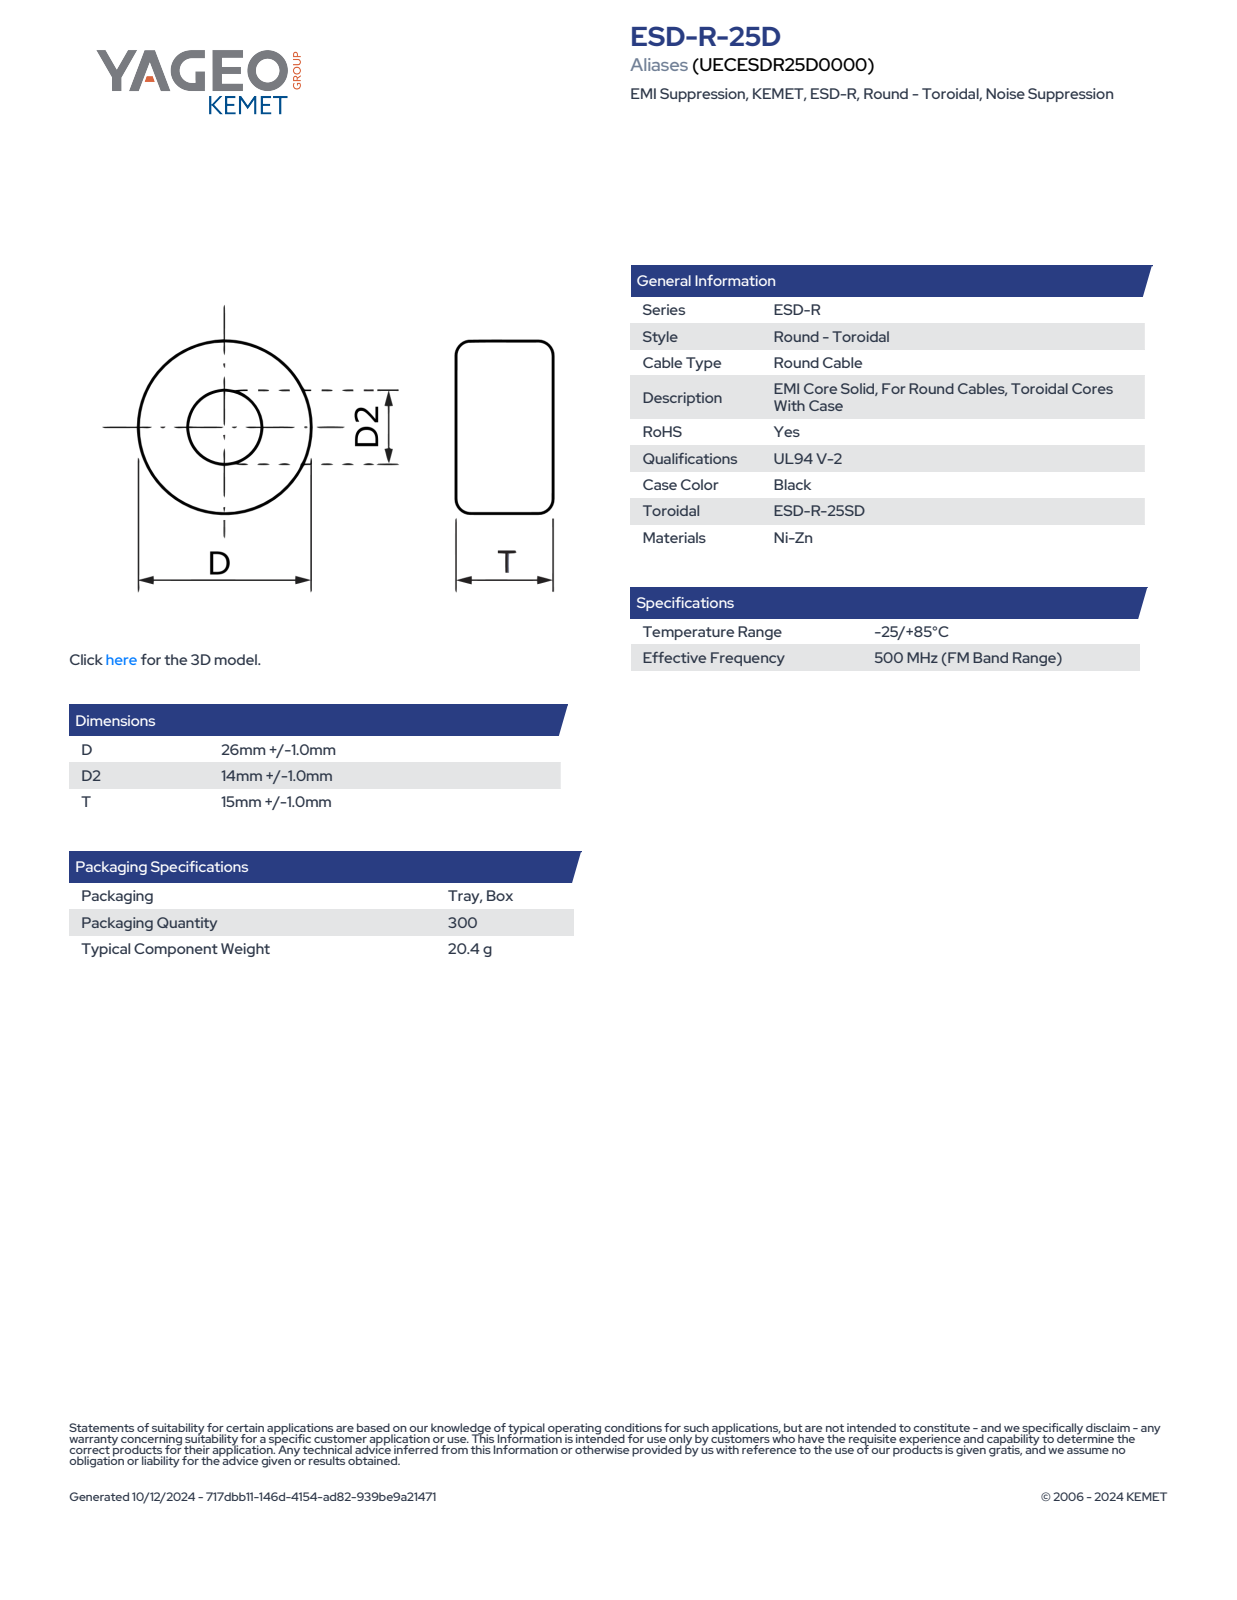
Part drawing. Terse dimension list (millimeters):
name: EC_KBC_D27D214T16
written by: SolidWorks 2021 (AUTOMOTIVE_DESIGN)
unit: mm
bodies: 1 solid, 66 faces (24 planar, 7 cylindrical, 35 other)
size: 27.01 × 27 × 16
volume: 6 672 mm³; area: 2 843 mm²
holes: 1× ⌀14
bosses: 1× ⌀27
rounds: 1× R13.51
face distances: 16, 7.15, 8.85, 1.7, 0.32, 7.47, 8.53, 1.38, 1.06, 8.21
